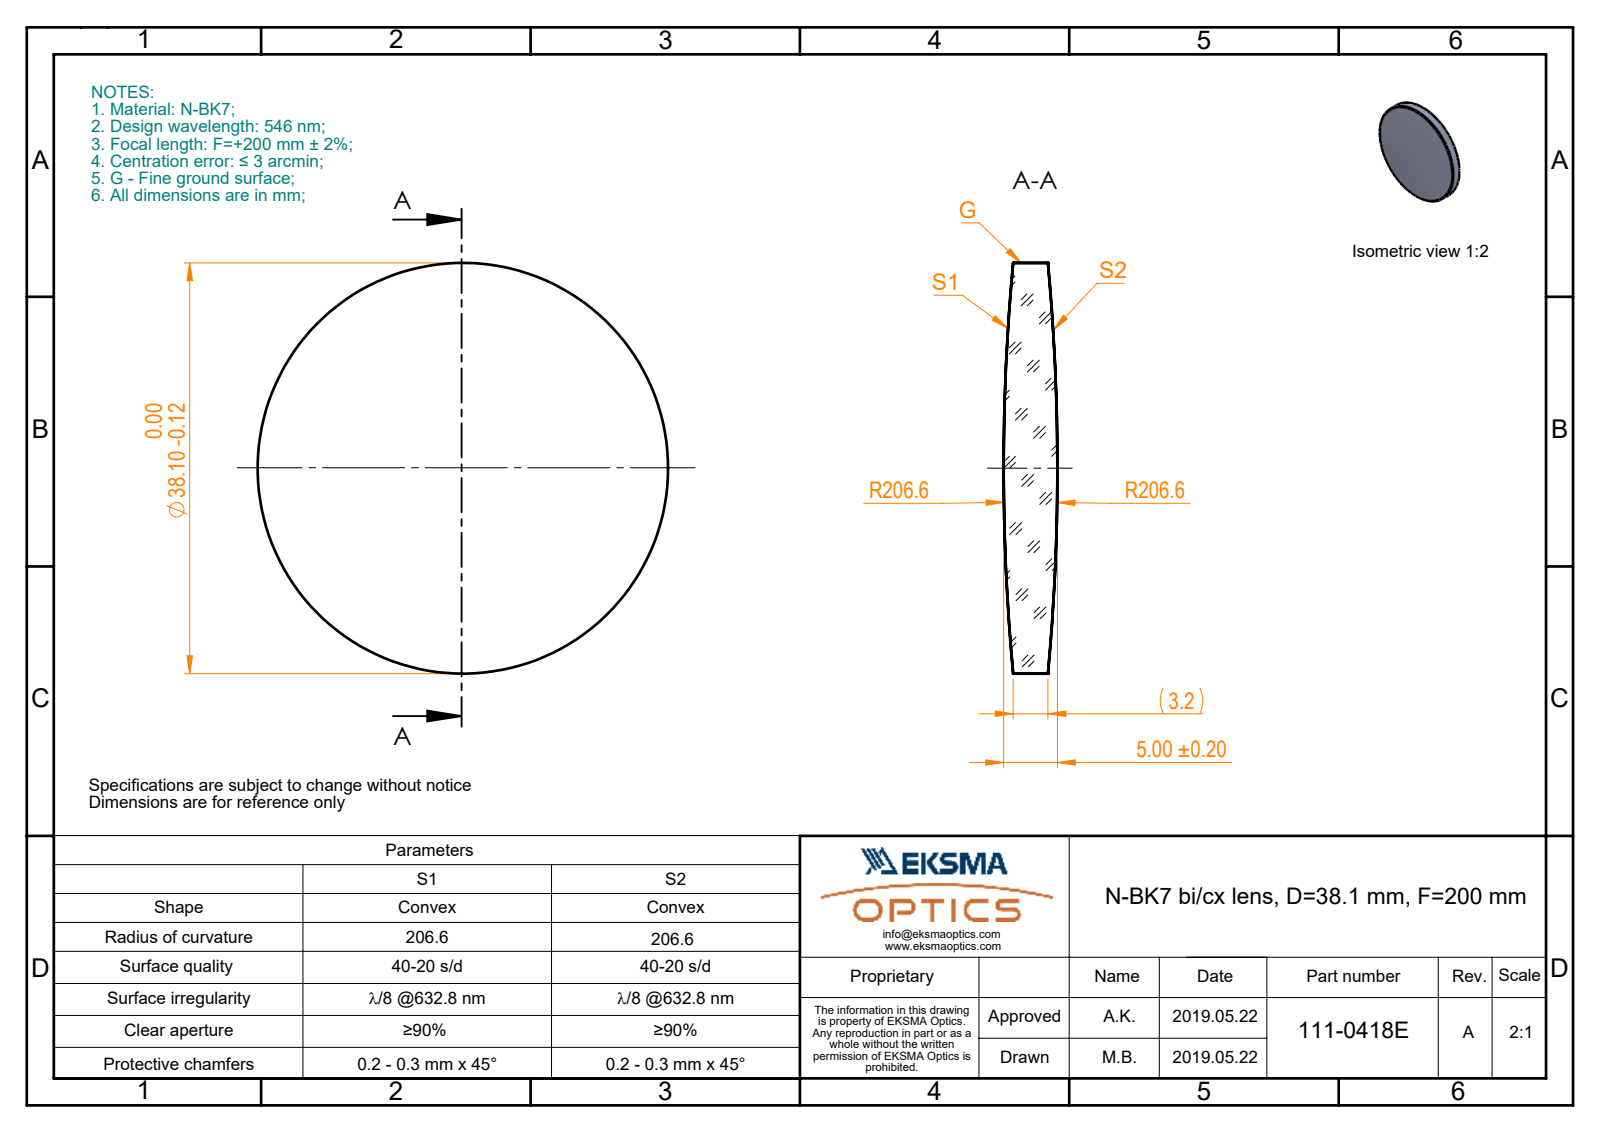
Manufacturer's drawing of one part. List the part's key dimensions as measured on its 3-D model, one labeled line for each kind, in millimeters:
Part name (STEP PRODUCT): 111-0418E BK7 bi-cx 38.1 F200
STEP written by: SolidWorks 2017 (CONFIG_CONTROL_DESIGN)
Units: millimetres
Bodies: 1 solid, 6 faces (0 planar, 2 cylindrical, 4 other)
Overall size (bounding box): 38.1 × 38.1 × 5
Volume: 4 698 mm³ · Surface area: 2 673 mm²
Round bosses / shafts (diameter × count): ⌀38.1 ×1
